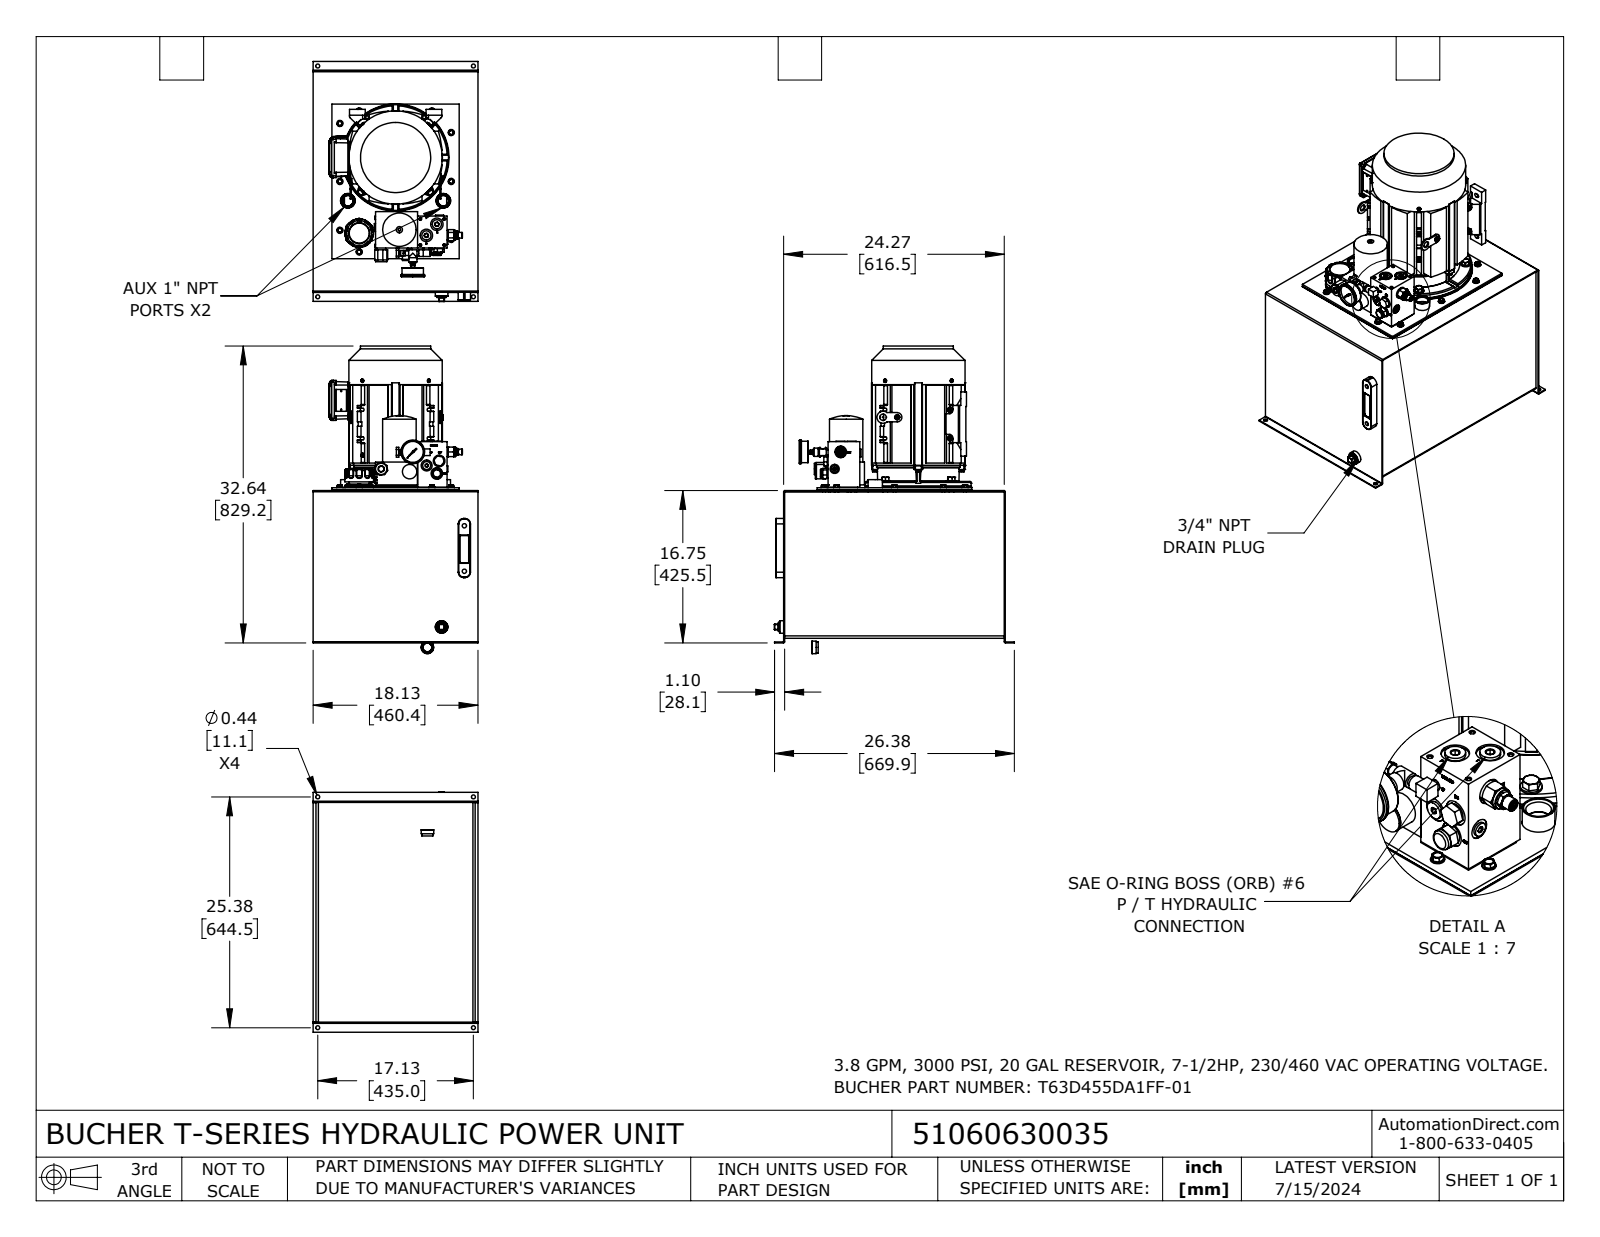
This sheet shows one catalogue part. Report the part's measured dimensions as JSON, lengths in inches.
{"part_name": "51060630035", "step_written_by": "SolidWorks 2023 (CONFIG_CONTROL_DESIGN)", "units": "inches", "bodies": {"solids": 119, "faces": 5112, "planar": 2513, "cylindrical": 1694, "other": 905}, "overall_size": [33.831, 26.4, 18.125], "volume_in3": 1700, "surface_area_in2": 6783, "round_holes": [[0.437, 19], [0.236, 11], [0.5, 11], [0.197, 10], [0.563, 10], [0.315, 9], [0.201, 8], [0.268, 8], [0.12, 6], [0.19, 6], [0.531, 6], [0.807, 5]], "round_bosses_or_shafts": [[0.676, 10], [0.313, 10], [0.551, 9], [0.472, 9], [0.373, 6], [0.5, 5], [0.25, 5], [1.062, 4]], "partial_cylinders_radius": [[0.02, 188], [0.079, 68], [0.039, 52], [0.25, 36], [0.063, 20], [0.118, 20], [0.375, 16], [0.05, 13]], "face_to_face_distances": [0.104, 0.105, 17.395, 16.135, 24.27, 17.5, 17.291, 16.239, 0.313, 24.375], "hole_center_spacings": [3.15, 3.469, 1.441, 1.442, 2.497, 6.232, 8.297, 0.78]}
